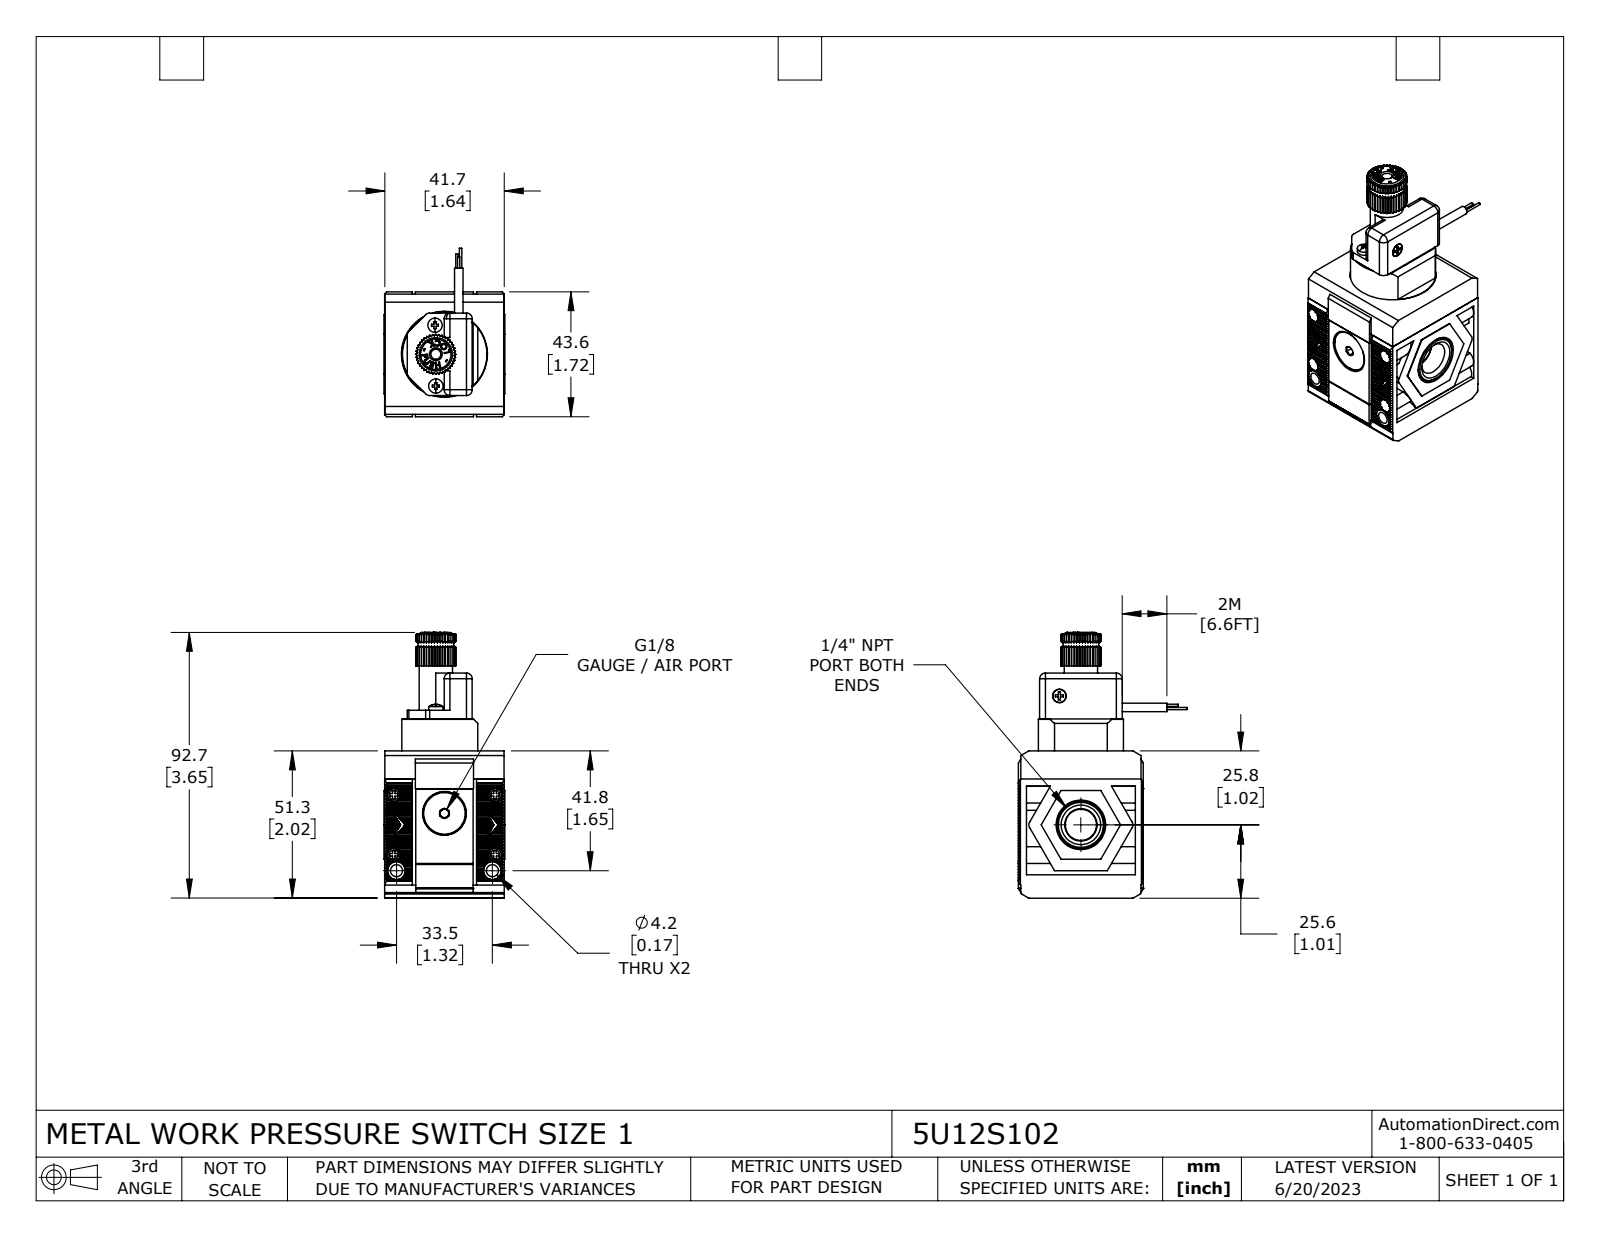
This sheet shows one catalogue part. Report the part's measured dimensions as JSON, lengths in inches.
{"part_name": "5U12S102", "step_written_by": "SolidWorks 2021 (CONFIG_CONTROL_DESIGN)", "units": "inches", "bodies": {"solids": 13, "faces": 1575, "planar": 1086, "cylindrical": 298, "other": 191}, "overall_size": [3.654, 2.315, 1.661], "volume_in3": 6.25, "surface_area_in2": 54.7, "round_holes": [[0.083, 4], [0.118, 4], [0.185, 4], [0.165, 2], [0.071, 1], [0.337, 1], [0.602, 1], [1.181, 1], [1.26, 1]], "round_bosses_or_shafts": [[0.181, 5], [0.102, 4], [0.031, 3], [0.244, 2], [0.197, 2], [1.169, 1], [0.898, 1], [0.717, 1]], "partial_cylinders_radius": [[0.079, 14], [0.024, 4], [0.122, 4], [0.008, 2], [0.008, 1], [0.009, 1], [0.009, 1], [0.009, 1]], "face_to_face_distances": [1.638, 1.339, 1.642, 0.307, 1.673, 0.386, 1.654, 0.043, 0.031, 1.646], "hole_center_spacings": [0.222, 0.742, 0.823, 0.9, 1.027, 1.042, 1.374, 1.394]}
